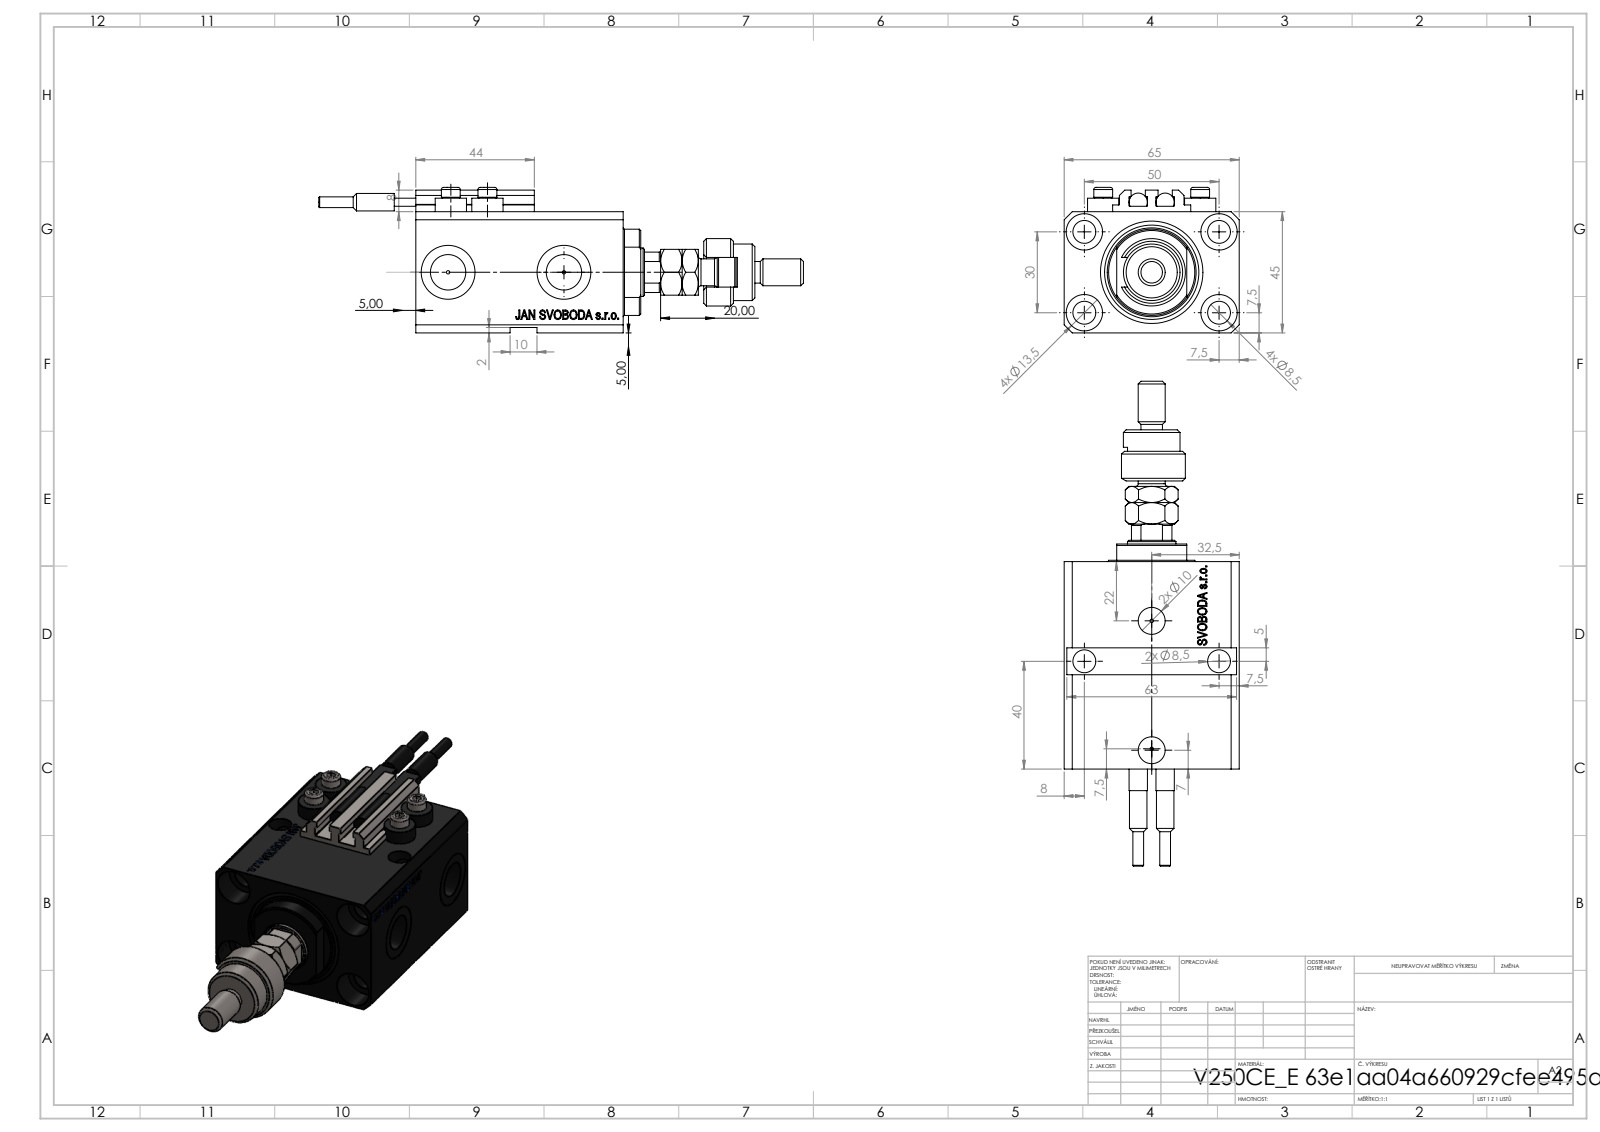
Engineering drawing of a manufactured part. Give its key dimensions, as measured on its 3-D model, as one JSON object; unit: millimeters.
{"part_name": "SWITCH_V250CE; MFA; V250CE_VC_E; V250CE_E_Body (+3 more)", "step_written_by": "SolidWorks 2019 (CONFIG_CONTROL_DESIGN)", "units": "millimeters", "bodies": {"solids": 12, "faces": 1220, "planar": 575, "cylindrical": 163, "other": 482}, "overall_size": [180, 65, 54], "volume_mm3": 211526, "surface_area_mm2": 68518, "round_holes": [[8.5, 7], [1.25, 4], [4, 4], [13.5, 4], [10, 2], [13.16, 2], [20, 2], [18, 1], [38, 1]], "round_bosses_or_shafts": [[11.6, 4], [7, 4], [6.8, 2], [6.5, 2], [4, 2], [25, 1], [21, 1], [16, 1]], "partial_cylinders_radius": [[0.2, 10], [5.5, 1], [8.5, 1], [8.75, 1], [16, 1]], "face_to_face_distances": [45, 14, 65, 63, 2, 77, 3, 5, 47, 6.9], "hole_center_spacings": [29.15, 50, 13.6, 15.12, 18.81, 18.97, 26.22, 26.61]}
